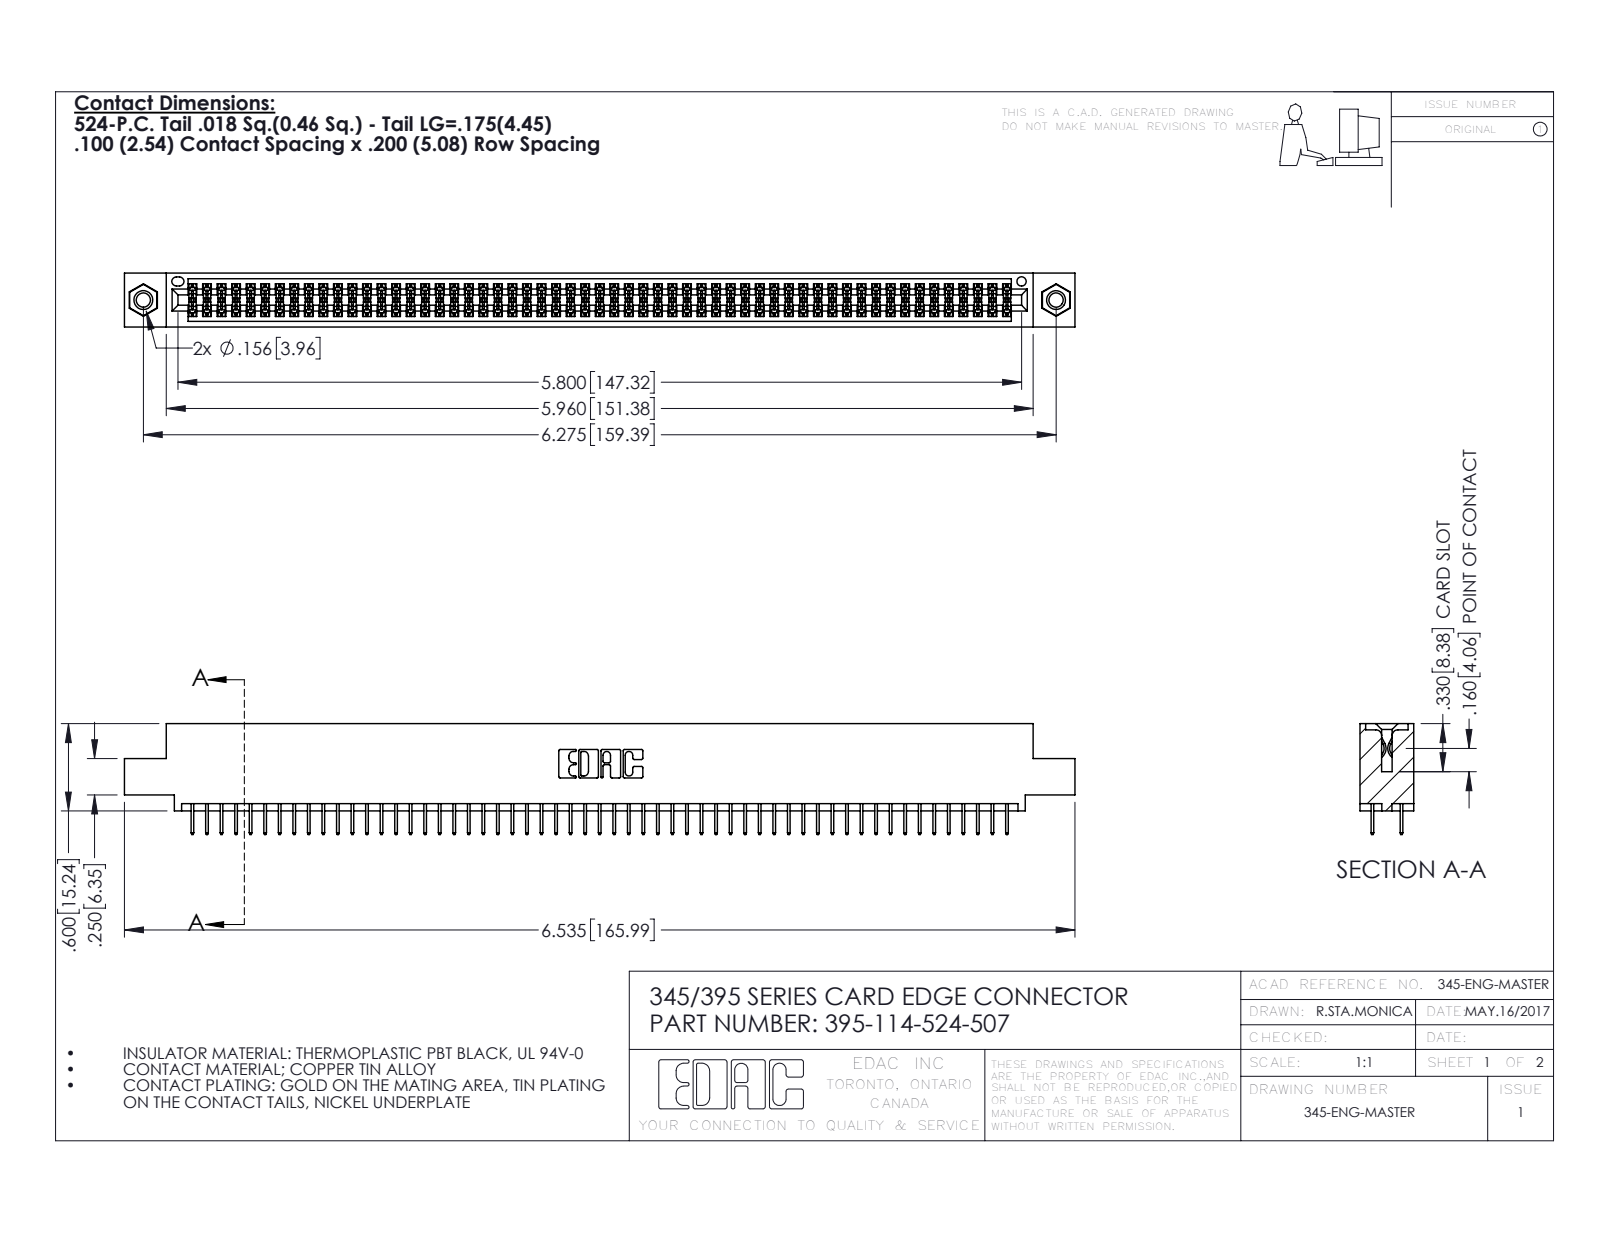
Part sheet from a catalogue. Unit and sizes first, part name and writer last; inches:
Units: inches
Overall size (bounding box): 6.535 × 0.762 × 0.37
Round holes (diameter × count): ⌀0.098 ×2, ⌀0.125 ×2, ⌀0.156 ×2, ⌀0.064 ×1
Round bosses / shafts (diameter × count): ⌀0.155 ×2
Partial cylindrical surfaces — rounded edges, fillets, slot ends (radius × count): R0.006 ×171, R0.01 ×22, R0.007 ×6, R0.031 ×6, R0.026 ×3, R0.014 ×2, R0.019 ×2, R0.022 ×2
Main face-to-face distances: 0.072, 0.298, 0.2, 0.37, 0.098, 0.272, 0.025, 0.225, 0.072, 0.175
Hole centre spacings: 0.27, 6.039, 6.275
Volume: 0.977 in³ · Surface area: 36.6 in²
Bodies: 117 solids, 6346 faces (4562 planar, 1768 cylindrical, 16 other)
Part name (STEP PRODUCT): 345-292-001_345-293-124; 345-250-001_345-250-005-103; 395-114-524-507; 345 Part_0.110 Offset - 0.156 Dia-TI
STEP written by: SolidWorks 2016 (CONFIG_CONTROL_DESIGN)
